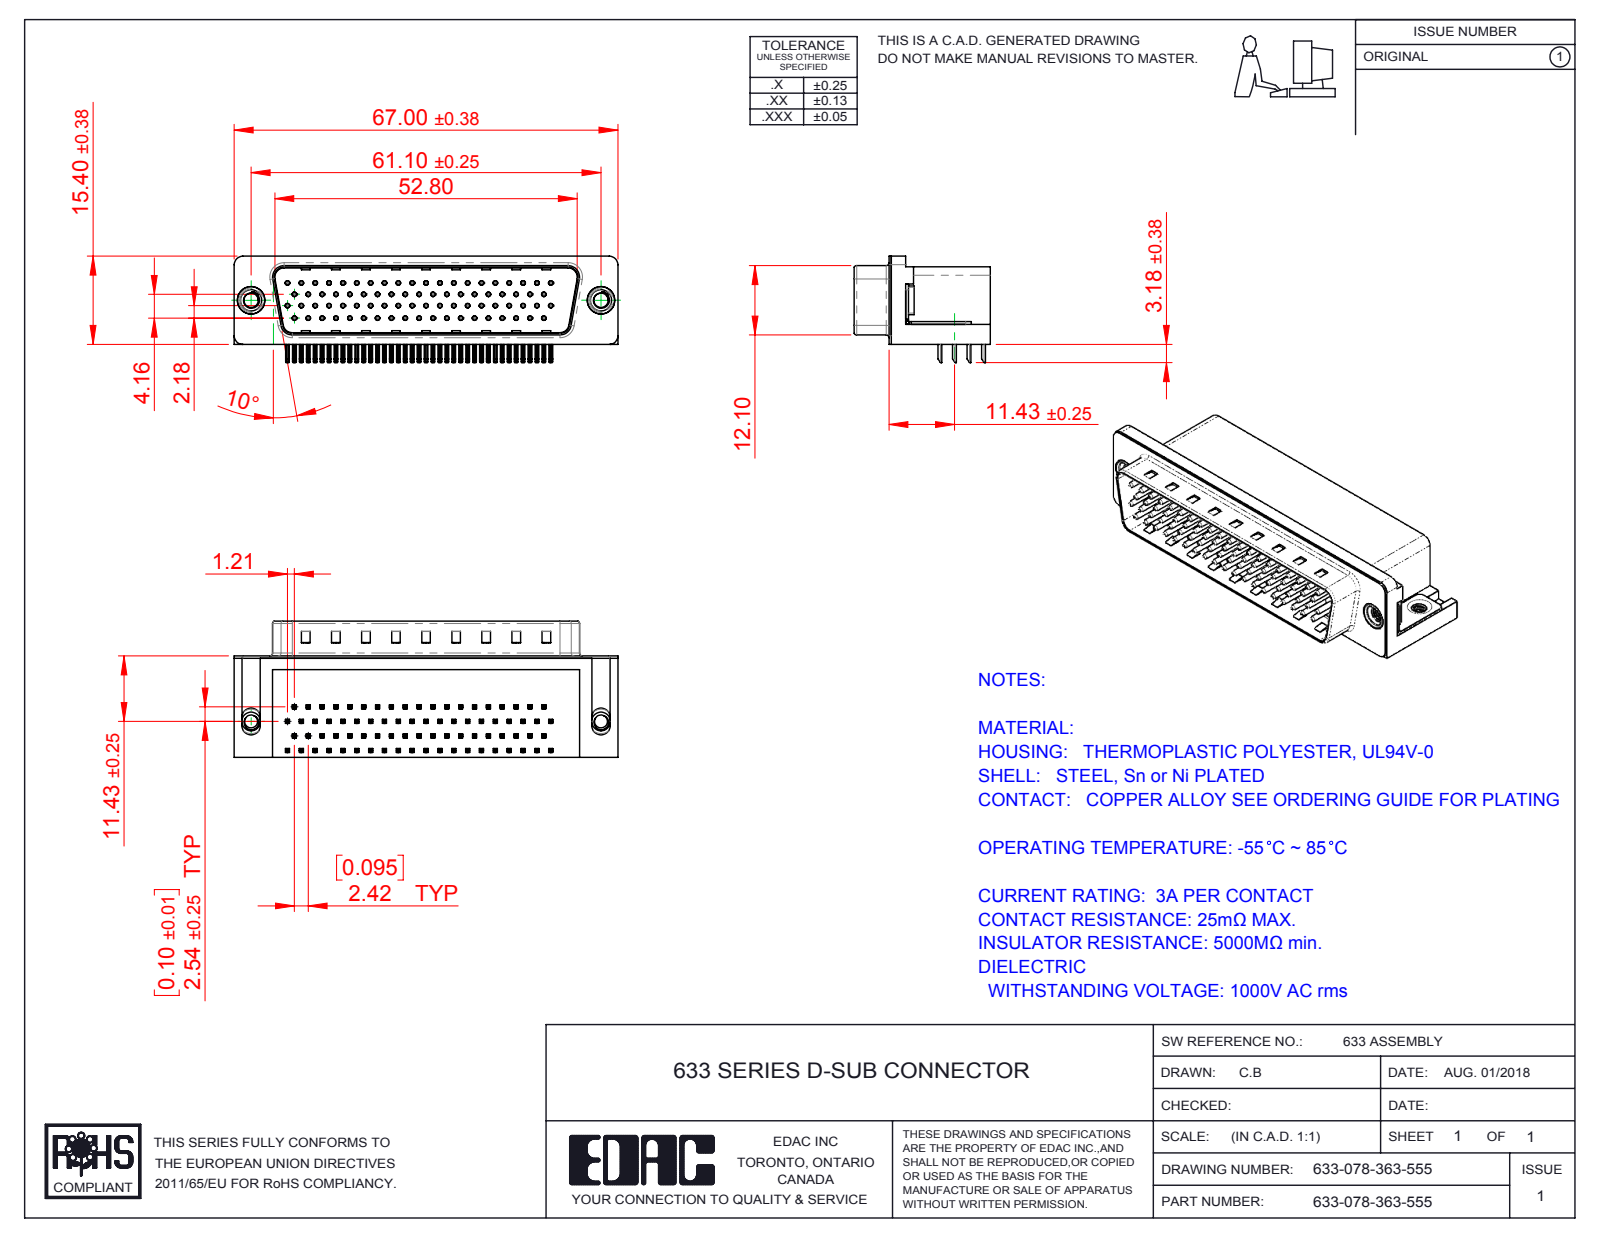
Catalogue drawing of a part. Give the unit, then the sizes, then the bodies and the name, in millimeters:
Units: millimetres
Overall size (bounding box): 67 × 23.8 × 18.58
Round holes (diameter × count): ⌀0.35 ×78, ⌀0.8 ×78, ⌀2.26 ×2, ⌀2.5 ×2, ⌀4 ×2, ⌀4.8 ×2, ⌀5 ×2
Round bosses / shafts (diameter × count): ⌀0.75 ×78, ⌀4.9 ×2, ⌀4.75 ×2, ⌀3.9 ×2, ⌀3.26 ×2
Partial cylindrical surfaces — rounded edges, fillets, slot ends (radius × count): R0.25 ×320, R0.12 ×156, R1 ×16, R0.5 ×9, R1.6 ×8, R1.5 ×6, R0.45 ×4, R0.9 ×4
Main face-to-face distances: 0.4, 13.2, 17.3, 11.7, 13.35, 2.05, 13.75, 1.65, 1.85, 11.9
Hole centre spacings: 2.42, 4.84, 7.26, 9.68, 6.26, 7.13, 12.1, 8.62
Volume: 14 619 mm³ · Surface area: 16 431 mm²
Bodies: 84 solids, 6306 faces (3981 planar, 1794 cylindrical, 531 other)
Part name (STEP PRODUCT): 633 M3 Threaded Rivet; 633 4-40 Threaded Board Mount_78 Contact; 633 Contact Top 78; 633-078-363-555 (+5 more)
STEP written by: SolidWorks 2016 (CONFIG_CONTROL_DESIGN)
